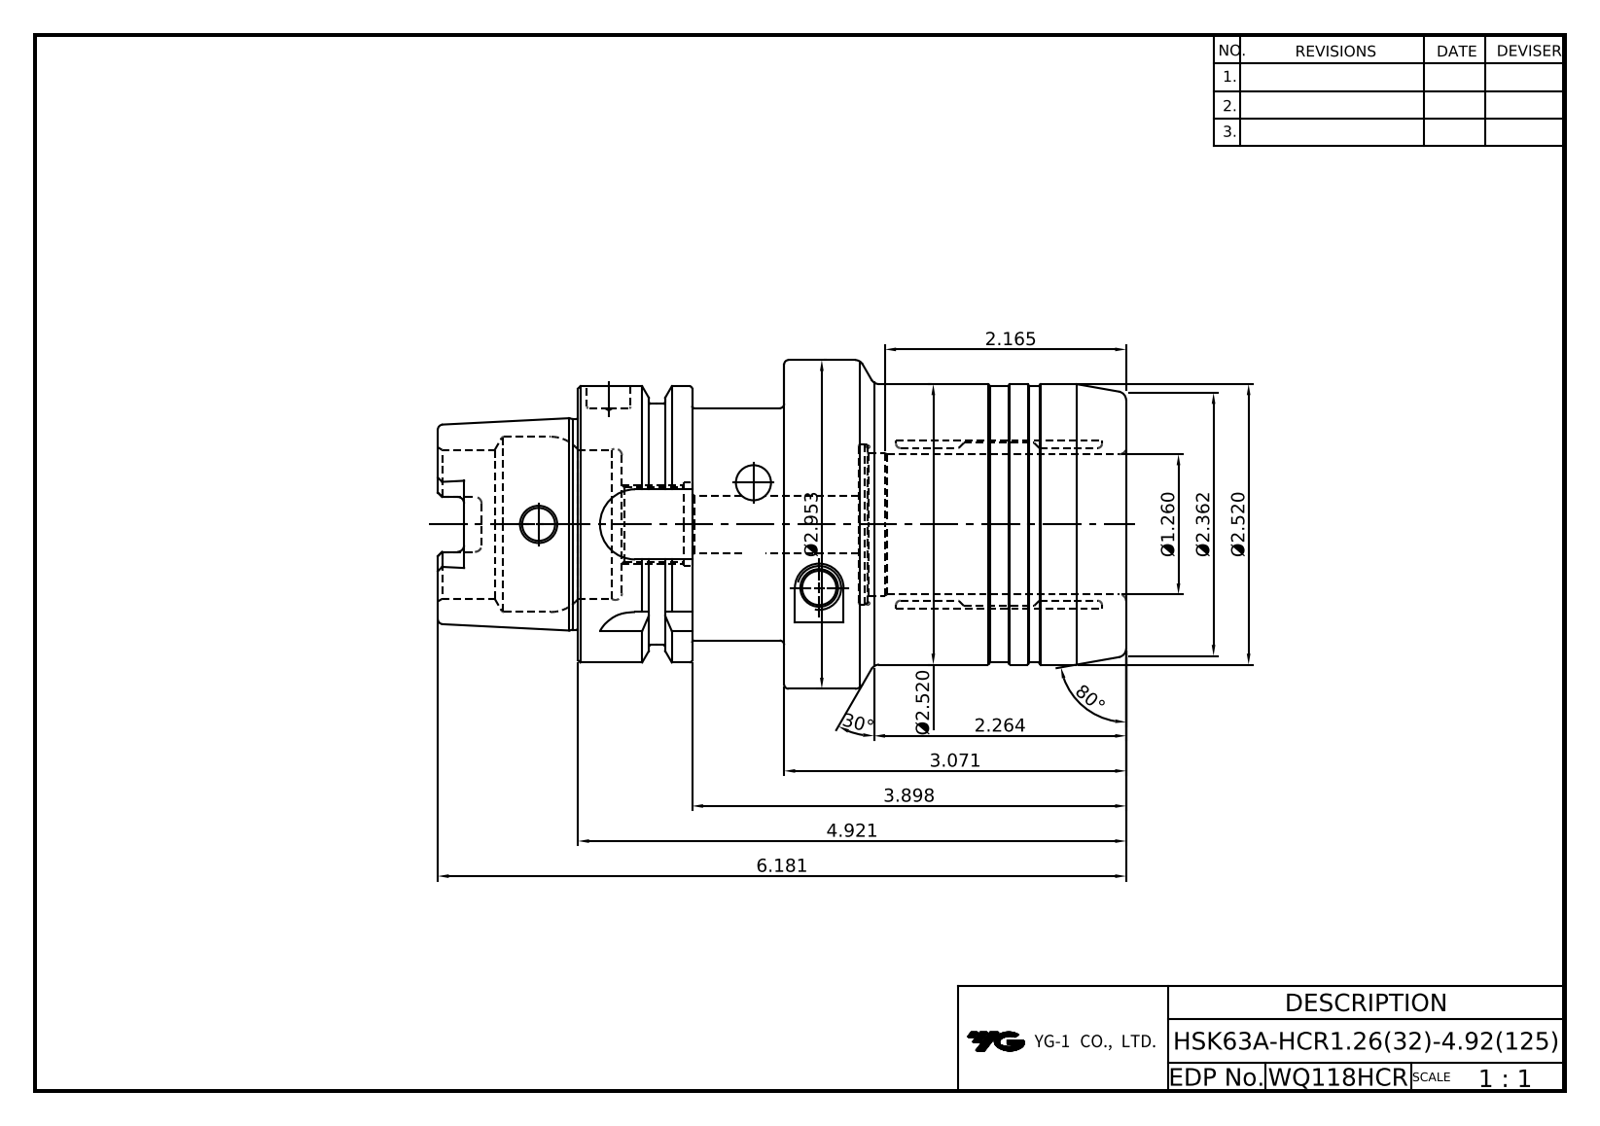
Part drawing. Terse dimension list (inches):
name: LO-HSK63A-HCR32-125
written by: Autodesk Inventor 2020 (AUTOMOTIVE_DESIGN)
unit: in
bodies: 1 solid, 142 faces (43 planar, 38 cylindrical, 61 other)
size: 6.181 × 2.953 × 2.953
volume: 21.64 in³; area: 82.58 in²
holes: 1× ⌀0.295, 1× ⌀0.394, 1× ⌀0.52, 1× ⌀0.666, 1× ⌀0.748, 1× ⌀1.26, 1× ⌀1.339, 1× ⌀1.575
bosses: 1× ⌀2.953, 1× ⌀2.52, 1× ⌀2.48, 1× ⌀2.165, 1× ⌀2.087, 1× ⌀1.891
rounds: 6× R0.059, 4× R0.113, 4× R0.315
face distances: 3.268, 1.654, 0.63, 4.921, 1.26, 0.866, 2.52, 1.024, 2.402, 1.496
